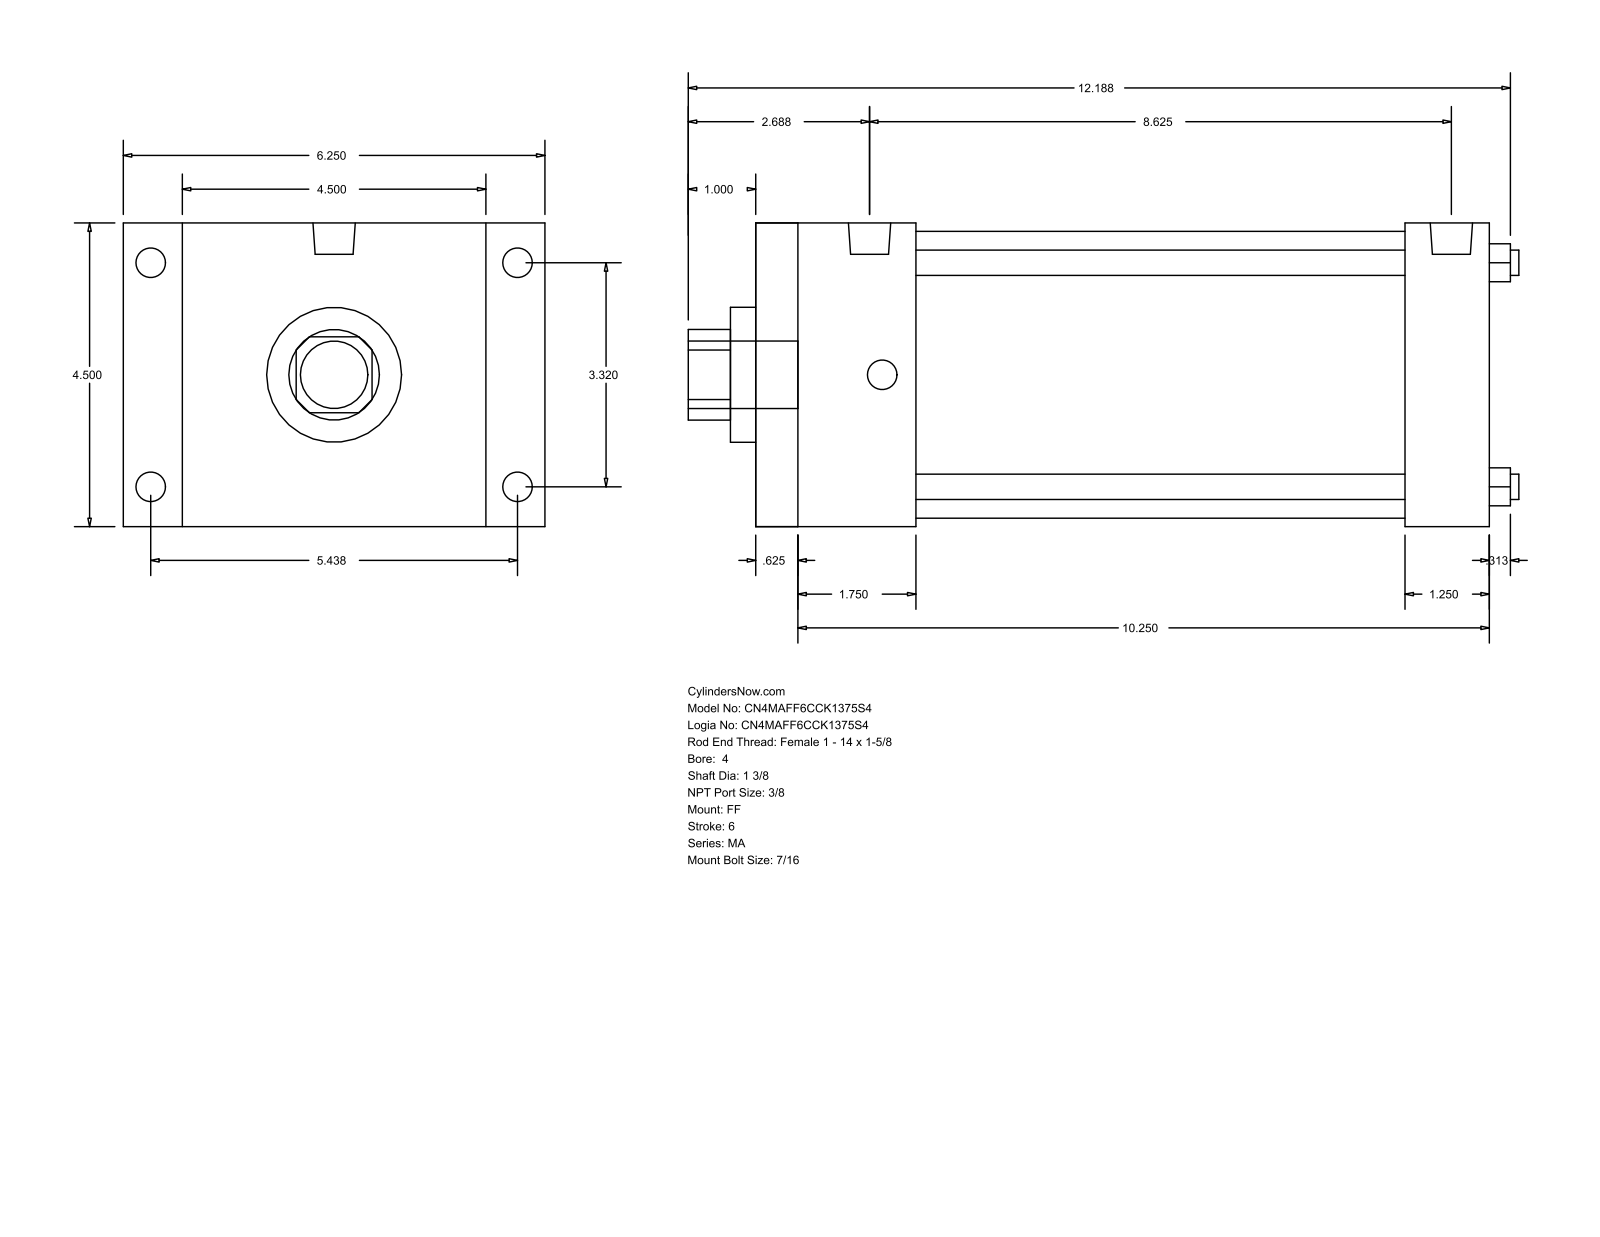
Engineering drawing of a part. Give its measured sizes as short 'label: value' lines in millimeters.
name: MA_FF__0400_1.375
written by: GSSL Pune (CONFIG_CONTROL_DESIGN)
unit: mm
bodies: 0 solids, 92 faces (64 planar, 28 cylindrical, 0 other)
size: 312.74 × 158.75 × 114.3
holes: 4× ⌀9.53, 1× ⌀34.92, 1× ⌀50.8, 1× ⌀107.95
bosses: 8× ⌀11.11, 2× ⌀15.93, 1× ⌀25.4
rounds: 1× R17.06
face distances: 114.3, 276.22, 15.87, 260.35, 22.23, 136.53, 244.48, 228.61, 31.74, 60.32
hole spacings: 59.62, 84.32, 119.25
